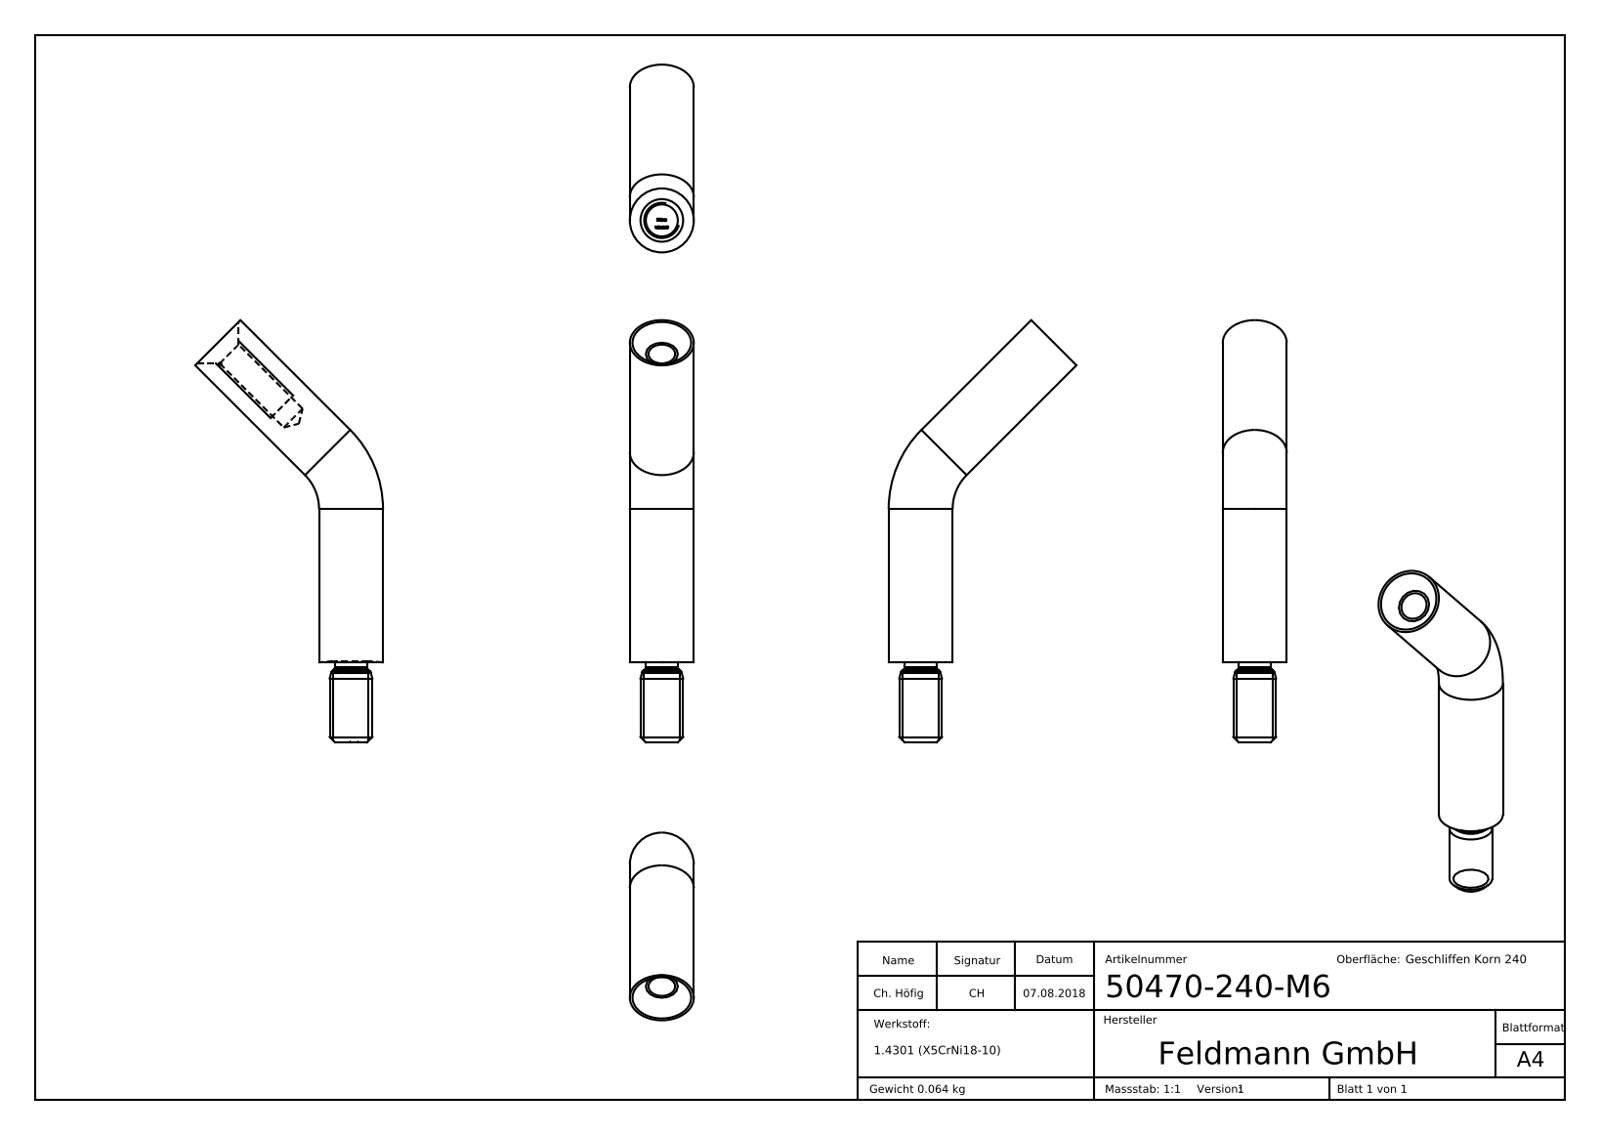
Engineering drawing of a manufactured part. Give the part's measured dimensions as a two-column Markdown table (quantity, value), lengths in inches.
| quantity | value |
| --- | --- |
| part name | 50470-240-M6 |
| STEP written by | SolidWorks 2015 (CONFIG_CONTROL_DESIGN) |
| units | inches |
| bodies | 1 solid, 283 faces (153 planar, 10 cylindrical, 120 other) |
| overall size | 3.12 × 1.387 × 0.472 |
| volume | 0.493 in³ |
| surface area | 5.485 in² |
| round holes (diameter × count) | 0.197 × 1 |
| round bosses / shafts (diameter × count) | 0.472 × 2, 0.315 × 1, 0.236 × 1 |
| main face-to-face distances | 0.052, 0.057, 0.044, 0.053, 0.019, 0.013, 0.023, 0.021, 0.017, 0.058 |
